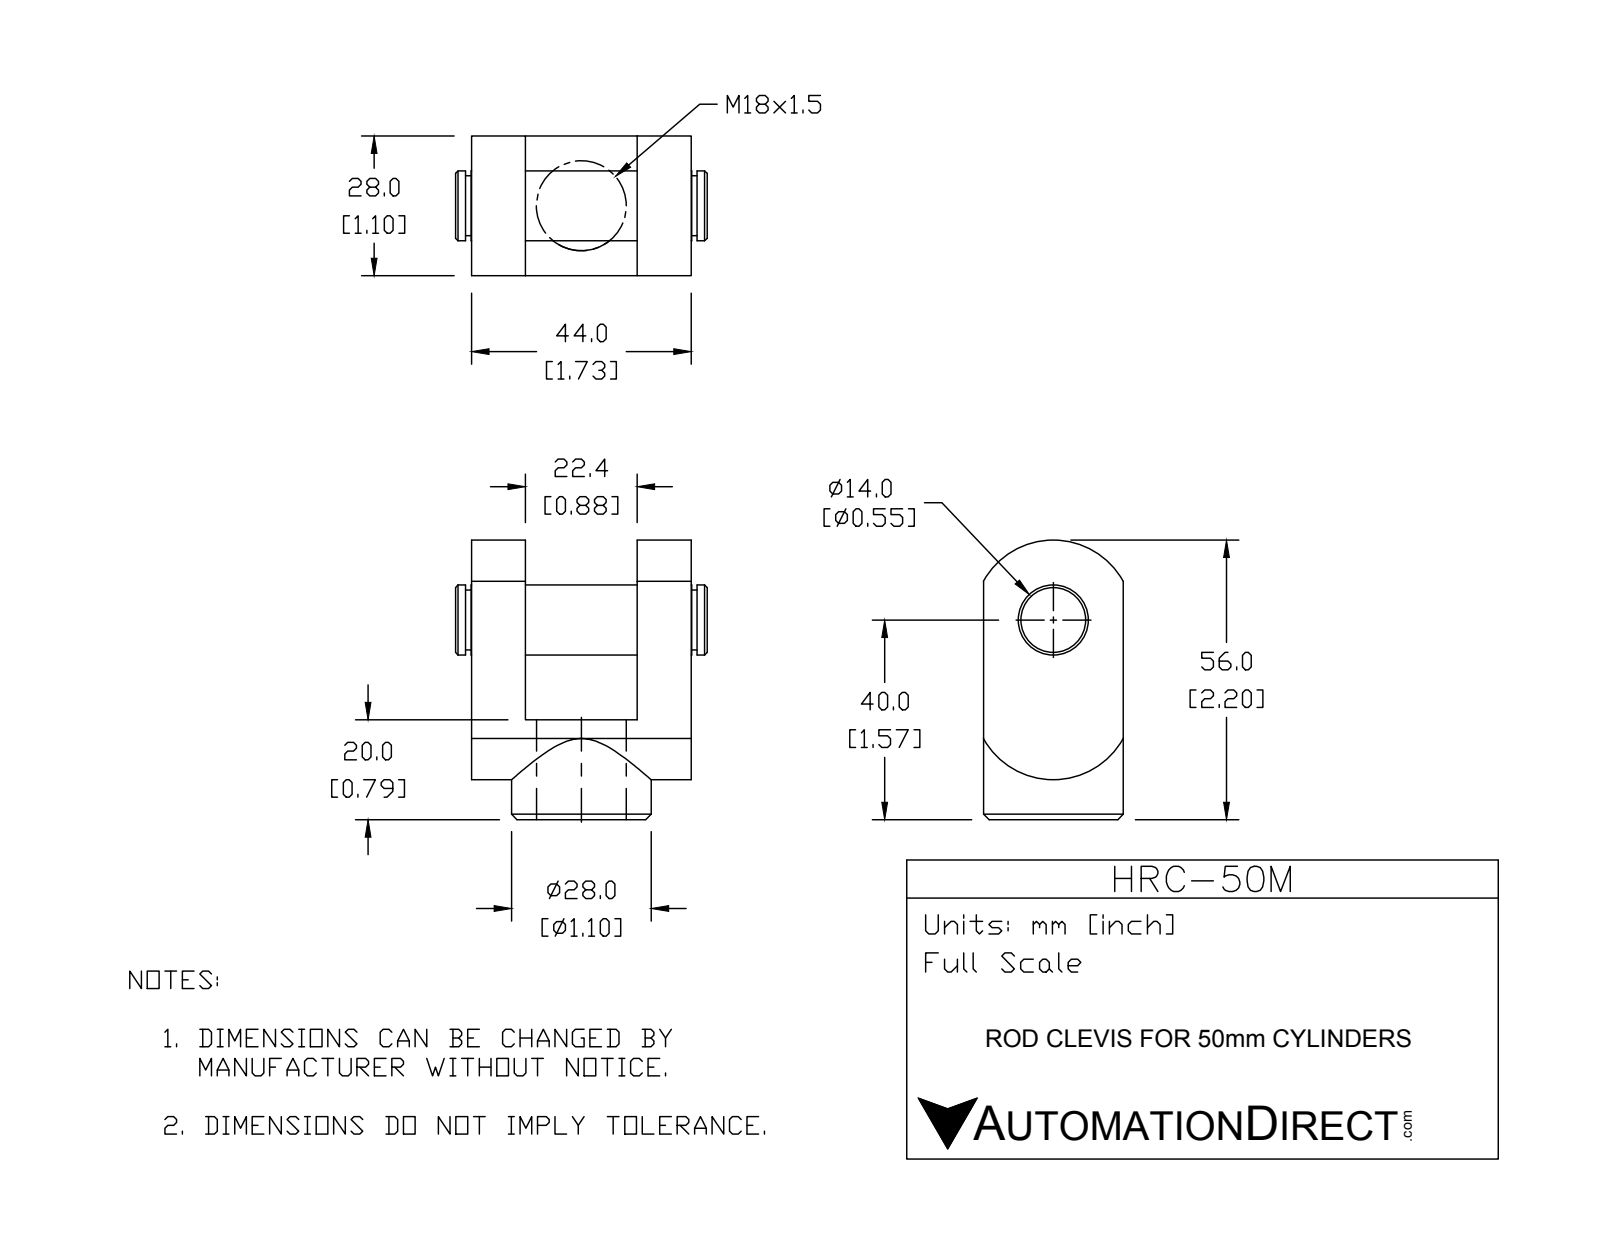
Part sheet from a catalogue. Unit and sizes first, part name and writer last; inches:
Units: inches
Overall size (bounding box): 2.205 × 1.984 × 1.102
Round holes (diameter × count): ⌀0.65 ×1
Round bosses / shafts (diameter × count): ⌀1.102 ×1, ⌀0.551 ×1, ⌀0.472 ×1
Partial cylindrical surfaces — rounded edges, fillets, slot ends (radius × count): R0.63 ×2
Main face-to-face distances: 0.425, 1.307, 1.732, 0.882, 1.102, 0.787, 0.126, 0.551, 1.433, 1.858
Volume: 2.327 in³ · Surface area: 20.35 in²
Bodies: 2 solids, 46 faces (14 planar, 22 cylindrical, 10 other)
Part name (STEP PRODUCT): HRC-50M
STEP written by: SolidWorks 2015 (CONFIG_CONTROL_DESIGN)
